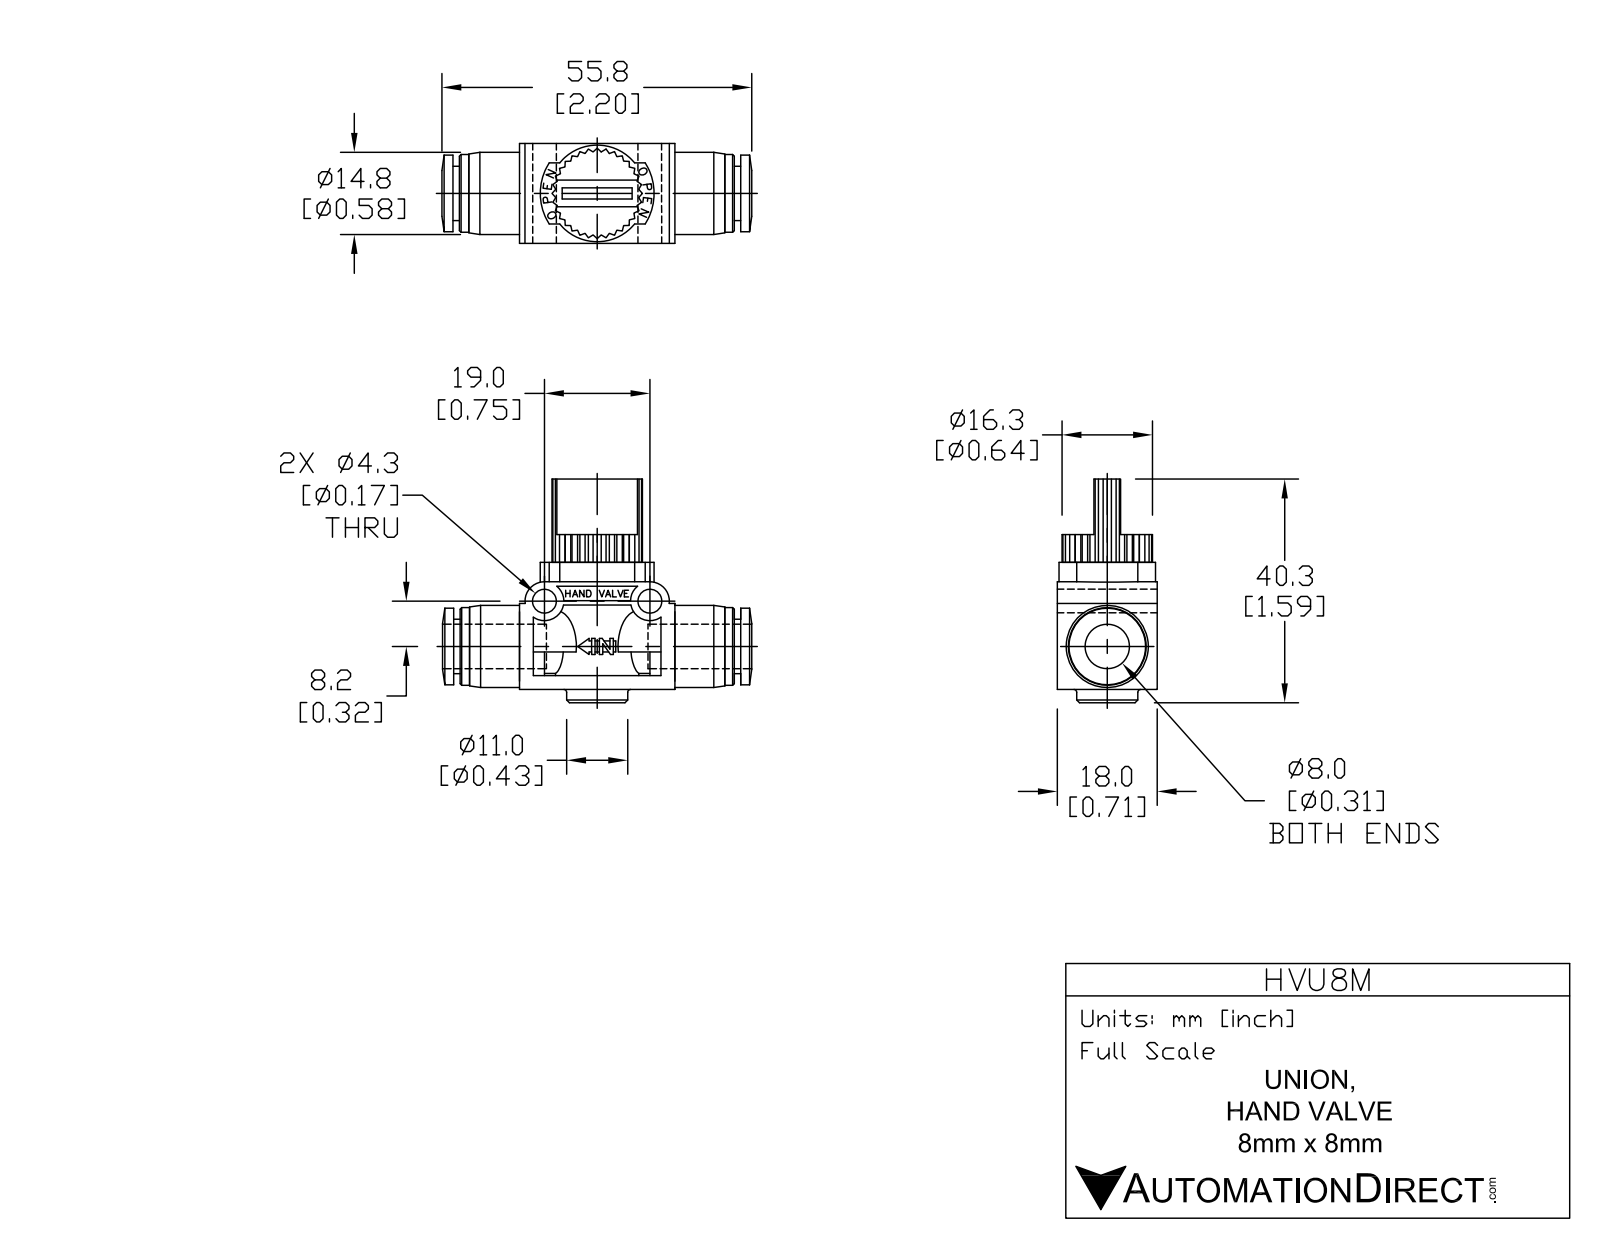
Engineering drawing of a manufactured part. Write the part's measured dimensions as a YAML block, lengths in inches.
part_name: "HVU8M"
step_written_by: "SolidWorks 2015 (AUTOMOTIVE_DESIGN)"
units: inches
bodies: {solids: 1, faces: 278, planar: 177, cylindrical: 77, other: 24}
overall_size: [2.193, 1.587, 0.709]
volume: 0.751
surface_area: 11.91
round_holes:
  - {diameter: 0.169, count: 2}
  - {diameter: 0.327, count: 1}
round_bosses_or_shafts:
  - {diameter: 0.591, count: 1}
  - {diameter: 0.583, count: 1}
  - {diameter: 0.551, count: 1}
  - {diameter: 0.543, count: 1}
  - {diameter: 0.433, count: 1}
  - {diameter: 0.386, count: 1}
partial_cylinders:
  - {radius: 0.138, count: 2}
  - {radius: 0.189, count: 1}
  - {radius: 0.217, count: 1}
  - {radius: 0.256, count: 1}
  - {radius: 0.303, count: 1}
  - {radius: 0.311, count: 1}
  - {radius: 0.343, count: 1}
  - {radius: 0.404, count: 1}
face_to_face_distances: [0.098, 0.26, 0.449, 0.134, 0.394, 0.315, 0.469, 0.055, 0.709, 0.079]
hole_center_spacings: [0.748]
